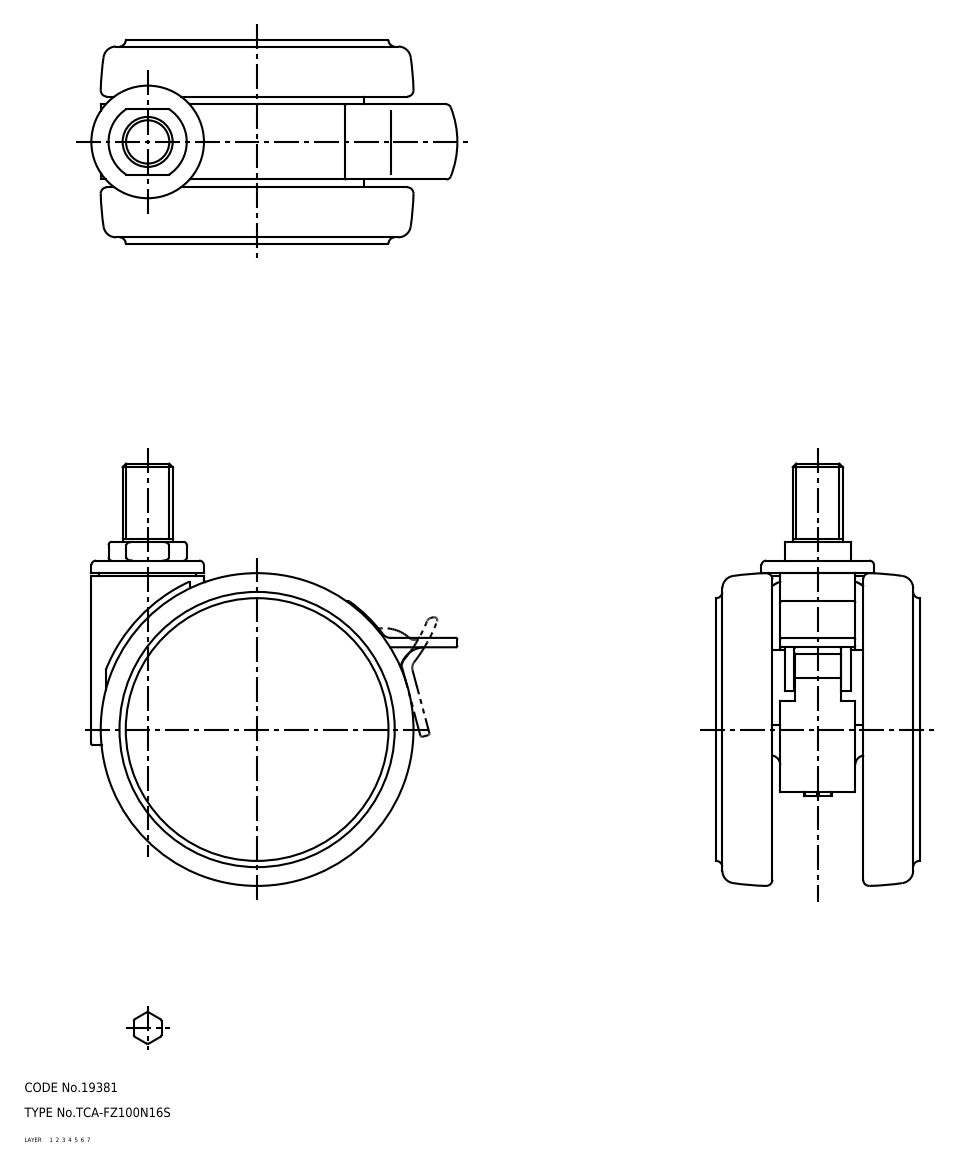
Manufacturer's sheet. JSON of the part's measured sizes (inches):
{"part_name": "caster; TCA-FZ100N16S", "step_written_by": "SolidWorks 2015 (AUTOMOTIVE_DESIGN)", "units": "inches", "bodies": {"solids": 1, "faces": 2495, "planar": 865, "cylindrical": 1191, "other": 439}, "overall_size": [5.315, 4.607, 2.567], "volume_in3": 18.7, "surface_area_in2": 194.3, "round_holes": [[0.11, 1], [0.118, 1], [0.13, 1], [0.161, 1], [0.165, 1], [0.236, 1], [0.358, 1], [0.394, 1], [0.398, 1], [0.413, 1], [0.433, 1], [0.472, 1]], "round_bosses_or_shafts": [[3.457, 1], [1.417, 1], [1.22, 1], [1.098, 1], [1.087, 1], [0.787, 1], [0.748, 1], [0.709, 1]], "partial_cylinders_radius": [[0.02, 236], [0.047, 160], [0.039, 87], [0.079, 25], [0.059, 23], [0.008, 18], [0.012, 12], [0.118, 8]], "face_to_face_distances": [0.071, 2.425, 2.496, 0.142, 2.354, 0.571, 0.642, 1.783, 0.713, 1.854], "hole_center_spacings": [0.897, 1.159, 1.732]}
